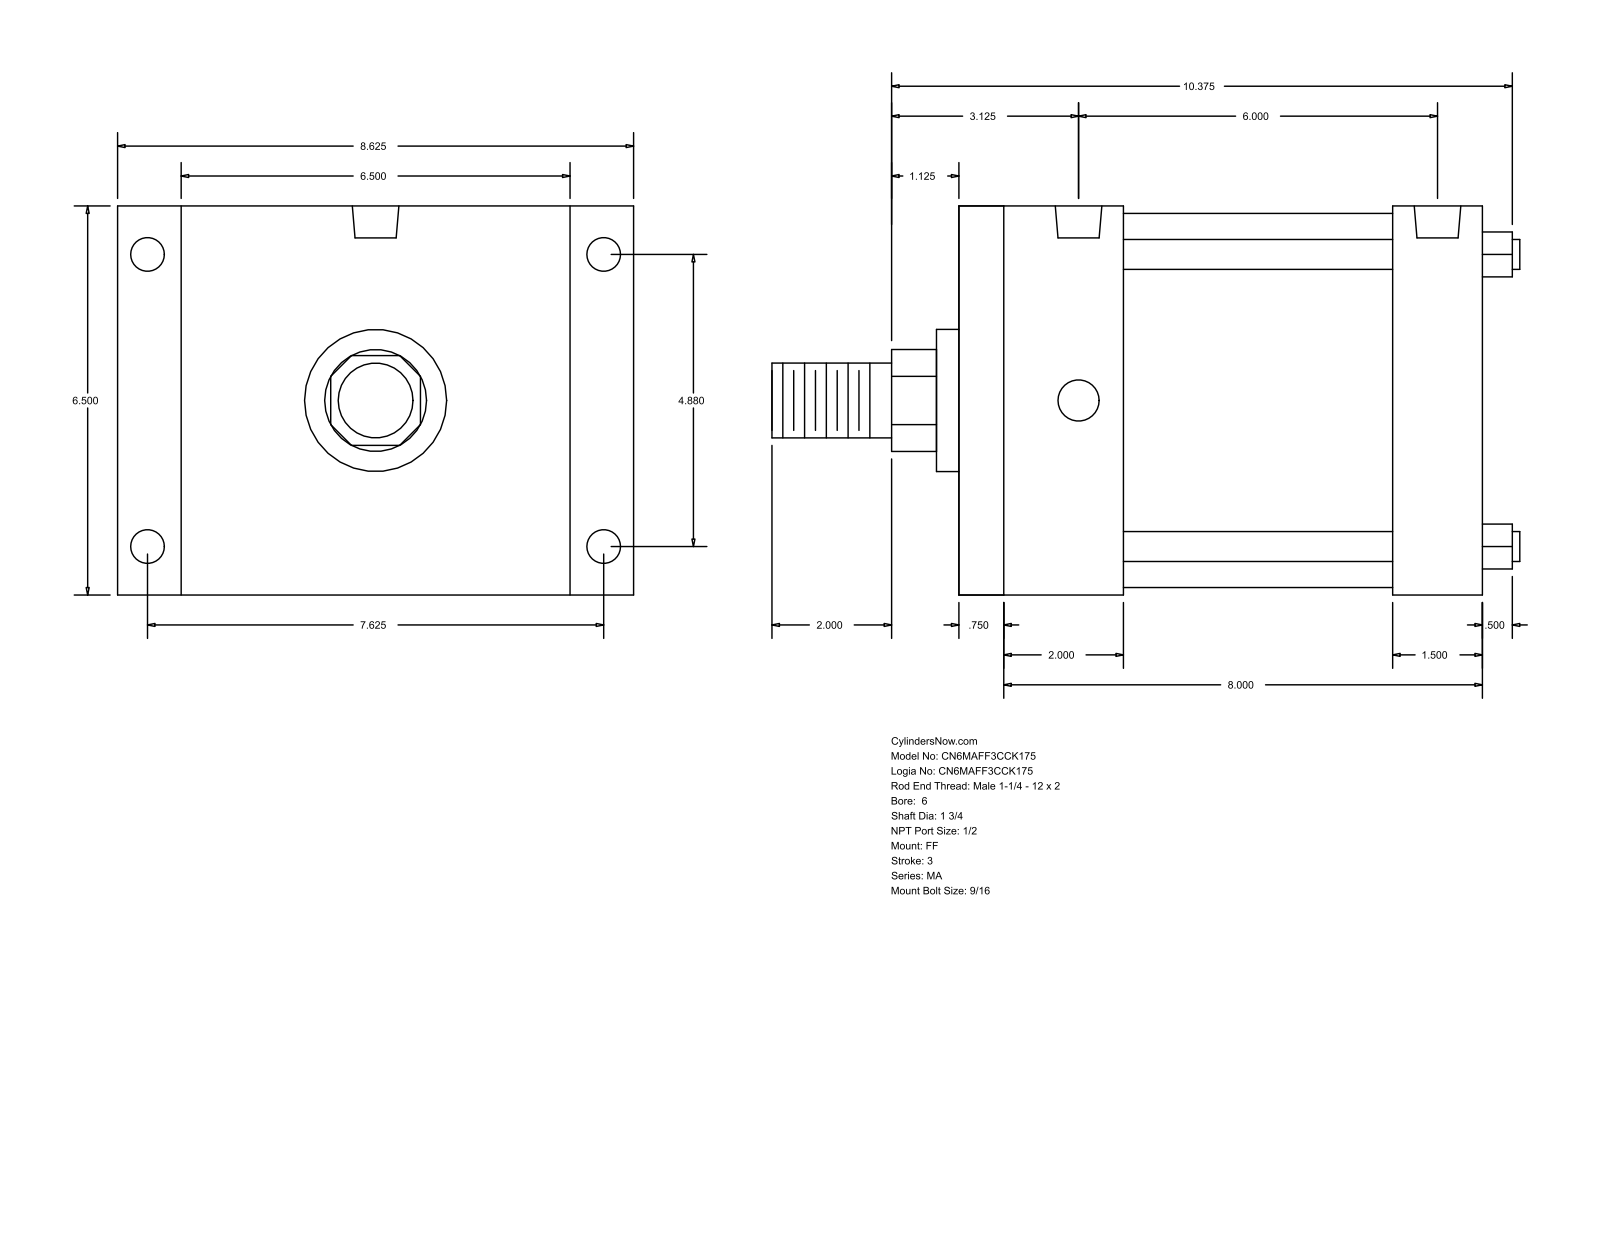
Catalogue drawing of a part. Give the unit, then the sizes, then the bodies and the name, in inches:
Units: inches
Overall size (bounding box): 12.5 × 8.625 × 6.5
Round holes (diameter × count): ⌀0.563 ×4, ⌀0.687 ×4, ⌀0.778 ×2
Round bosses / shafts (diameter × count): ⌀0.5 ×4, ⌀6.25 ×1, ⌀2.375 ×1, ⌀1.75 ×1, ⌀1.25 ×1
Partial cylindrical surfaces — rounded edges, fillets, slot ends (radius × count): R0.852 ×1
Main face-to-face distances: 6.5, 8.75, 0.75, 8, 2, 2.75, 1.5, 6, 7.25, 4.5
Hole centre spacings: 4.88, 6, 7.625, 9.053
Bodies: 0 solids, 92 faces (64 planar, 28 cylindrical, 0 other)
Part name (STEP PRODUCT): MA_FF__0600_1.75
STEP written by: GSSL Pune (CONFIG_CONTROL_DESIGN)
